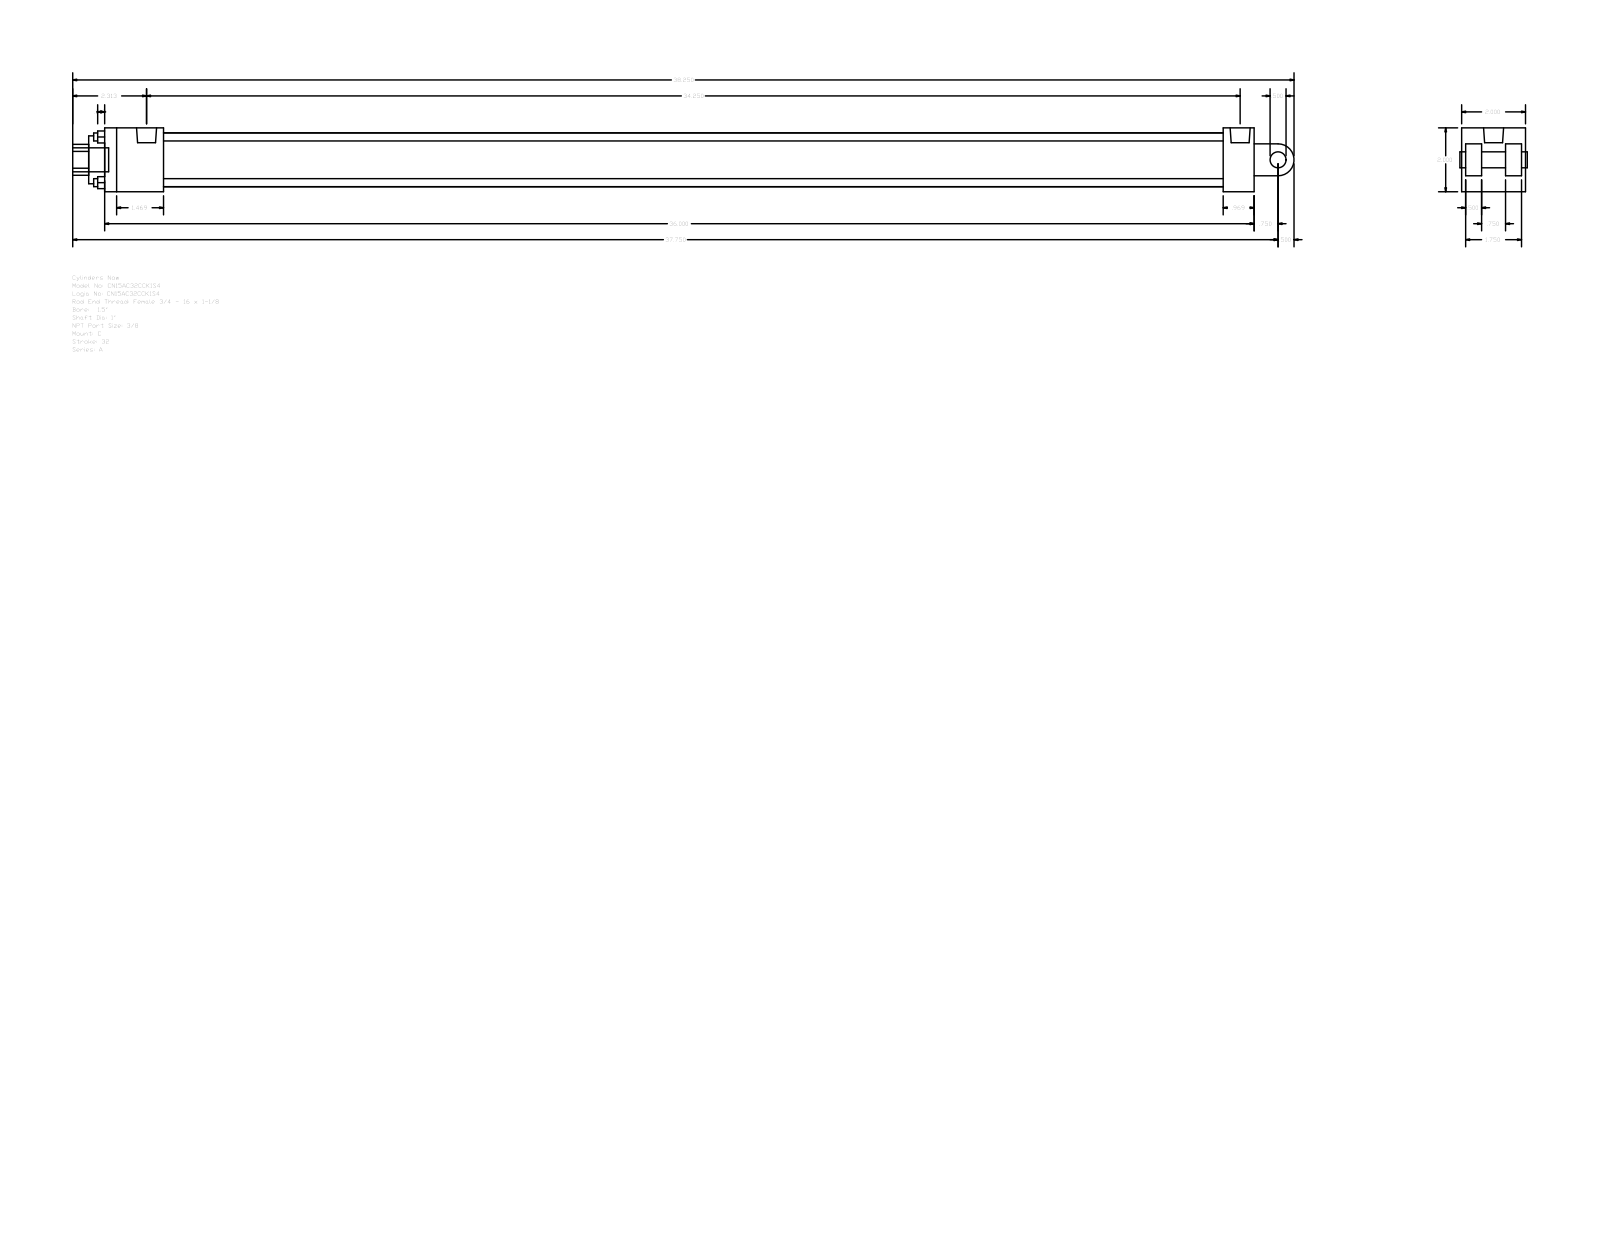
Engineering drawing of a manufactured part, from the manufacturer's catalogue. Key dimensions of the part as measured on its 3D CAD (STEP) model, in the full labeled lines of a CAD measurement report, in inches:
Part name (STEP PRODUCT): A_C__0150_1
STEP written by: GSSL Pune (CONFIG_CONTROL_DESIGN)
Units: inches
Bodies: 0 solids, 99 faces (70 planar, 29 cylindrical, 0 other)
Overall size (bounding box): 38.25 × 2 × 2
Round holes (diameter × count): ⌀0.25 ×4, ⌀0.219 ×2, ⌀0.627 ×1, ⌀1 ×1, ⌀1.5 ×1, ⌀1.69 ×1
Round bosses / shafts (diameter × count): ⌀0.219 ×2, ⌀0.75 ×1, ⌀0.627 ×1, ⌀0.5 ×1
Partial cylindrical surfaces — rounded edges, fillets, slot ends (radius × count): R0.484 ×1, R0.5 ×1
Main face-to-face distances: 2, 0.5, 0.125, 0.625, 1.875, 1.375, 1.25, 36, 35.031, 0.969
Hole centre spacings: 1.011, 1.43, 2.022, 0.156
